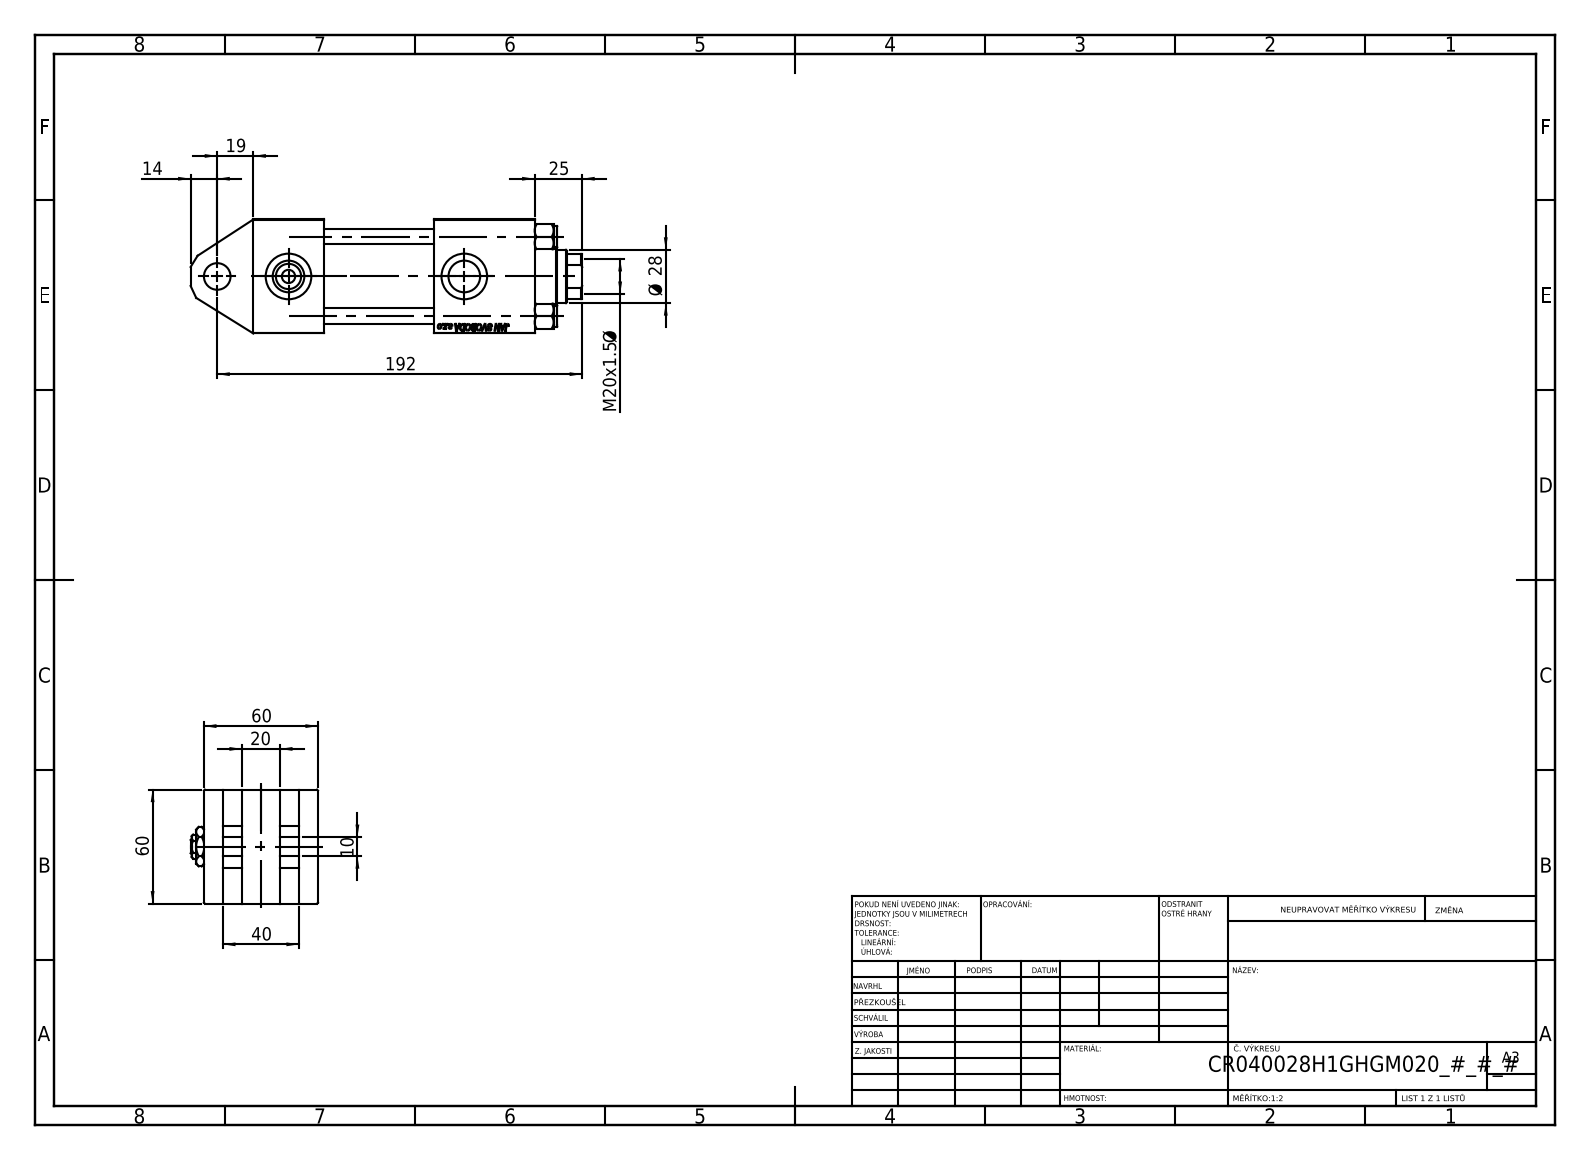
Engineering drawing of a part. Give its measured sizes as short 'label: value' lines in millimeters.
name: V215CR_H_Body; V215CR_TYCINKA_H; V215_VC_A; V215CR_VCP_H (+2 more)
written by: SolidWorks 2019 (CONFIG_CONTROL_DESIGN)
unit: mm
bodies: 12 solids, 1177 faces (542 planar, 87 cylindrical, 548 other)
size: 206 × 67 × 60
volume: 448 637 mm³; area: 119 962 mm²
holes: 4× ⌀8, 2× ⌀7, 2× ⌀16.66, 2× ⌀24, 1× ⌀14, 1× ⌀18.5, 1× ⌀28, 1× ⌀31, 1× ⌀40, 1× ⌀45
bosses: 4× ⌀11, 1× ⌀46, 1× ⌀42
rounds: 1× R13.5
face distances: 60, 10, 20, 40, 53, 37, 58, 50, 30, 95
hole spacings: 29.49, 41.7, 58.97, 37.5, 92.5, 130
